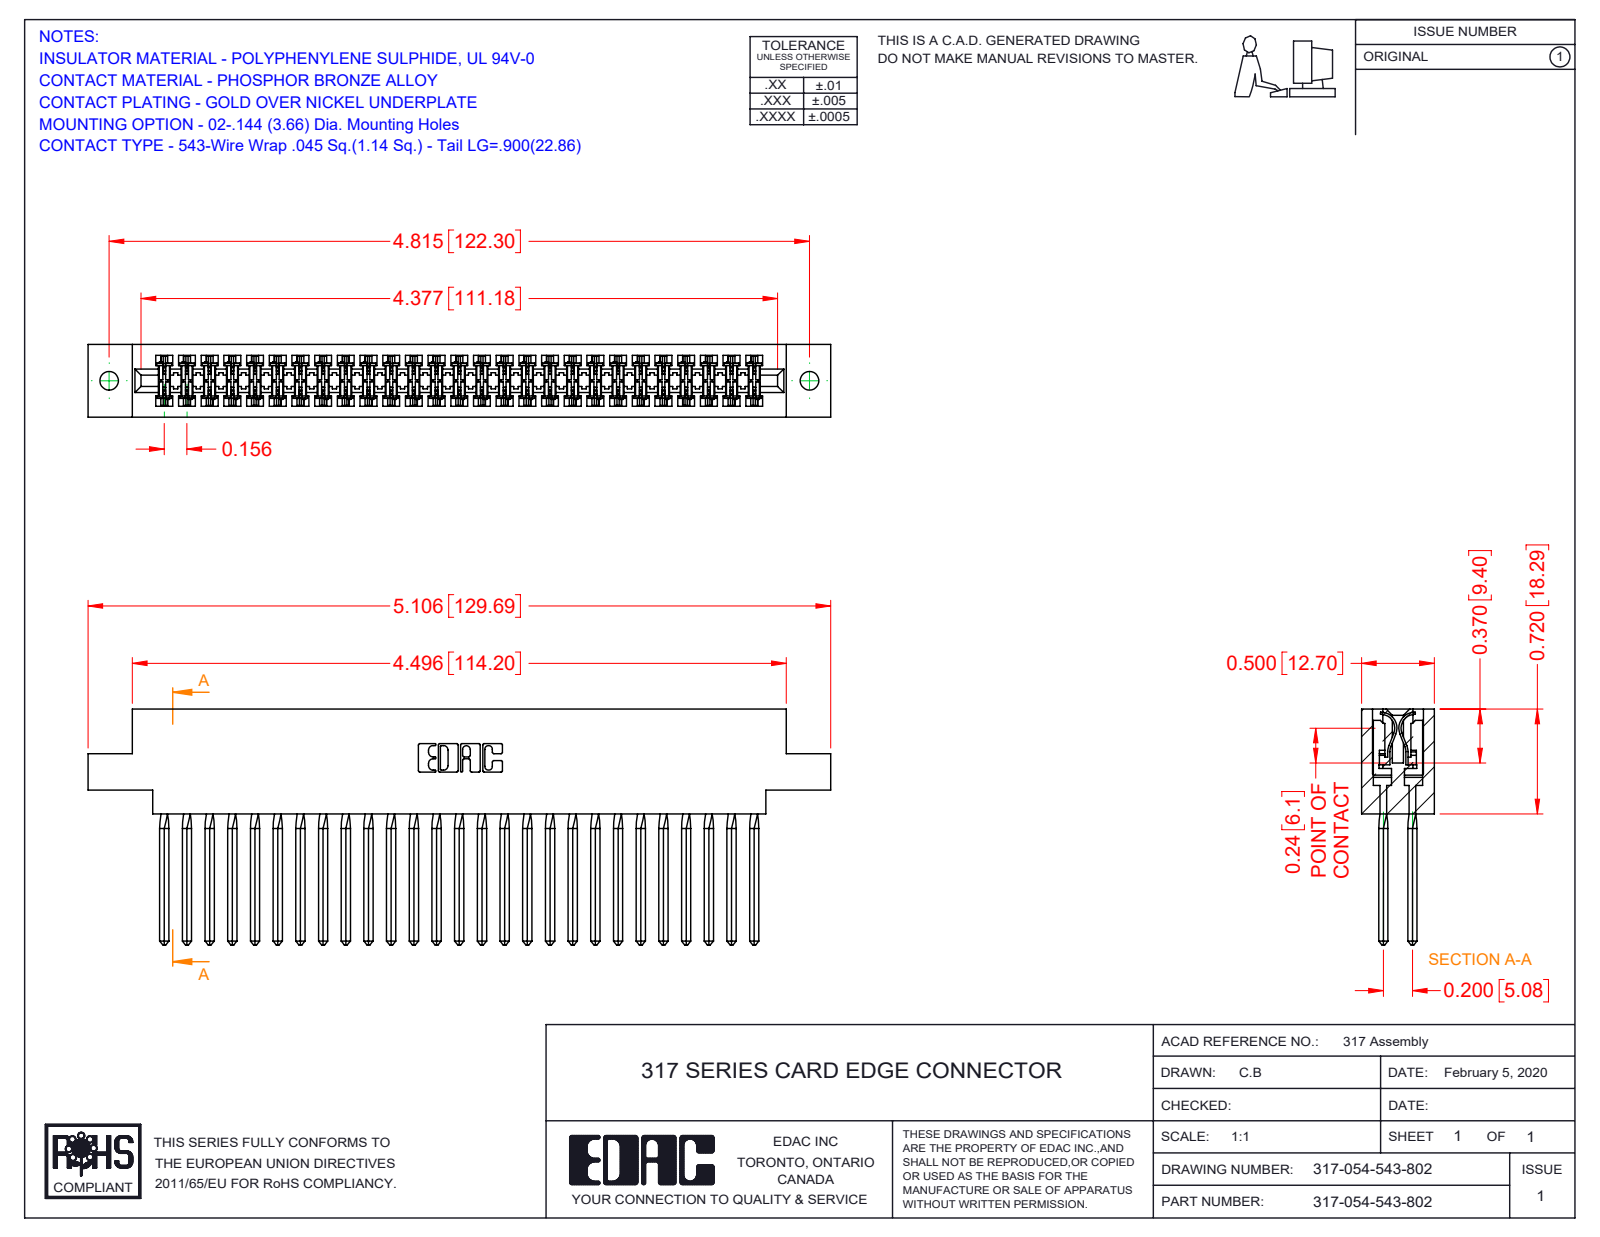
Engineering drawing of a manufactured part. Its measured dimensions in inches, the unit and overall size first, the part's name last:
Units: inches
Overall size (bounding box): 5.106 × 1.62 × 0.5
Round holes (diameter × count): ⌀0.128 ×2
Partial cylindrical surfaces — rounded edges, fillets, slot ends (radius × count): R0.015 ×108, R0.01 ×22, R0.007 ×6, R0.031 ×6, R0.026 ×3, R0.095 ×2, R0.1 ×2, R0.11 ×2
Main face-to-face distances: 0.5, 0.075, 0.425, 0.35, 0.11, 0.195, 0.094, 0.72, 0.2, 0.115
Hole centre spacings: 4.815
Volume: 1.311 in³ · Surface area: 49.21 in²
Bodies: 55 solids, 4908 faces (4000 planar, 692 cylindrical, 216 other)
Part name (STEP PRODUCT): 317-290-001_543; 317-054-543-802; 317 Part_.144 Dia
STEP written by: SolidWorks 2016 (CONFIG_CONTROL_DESIGN)
